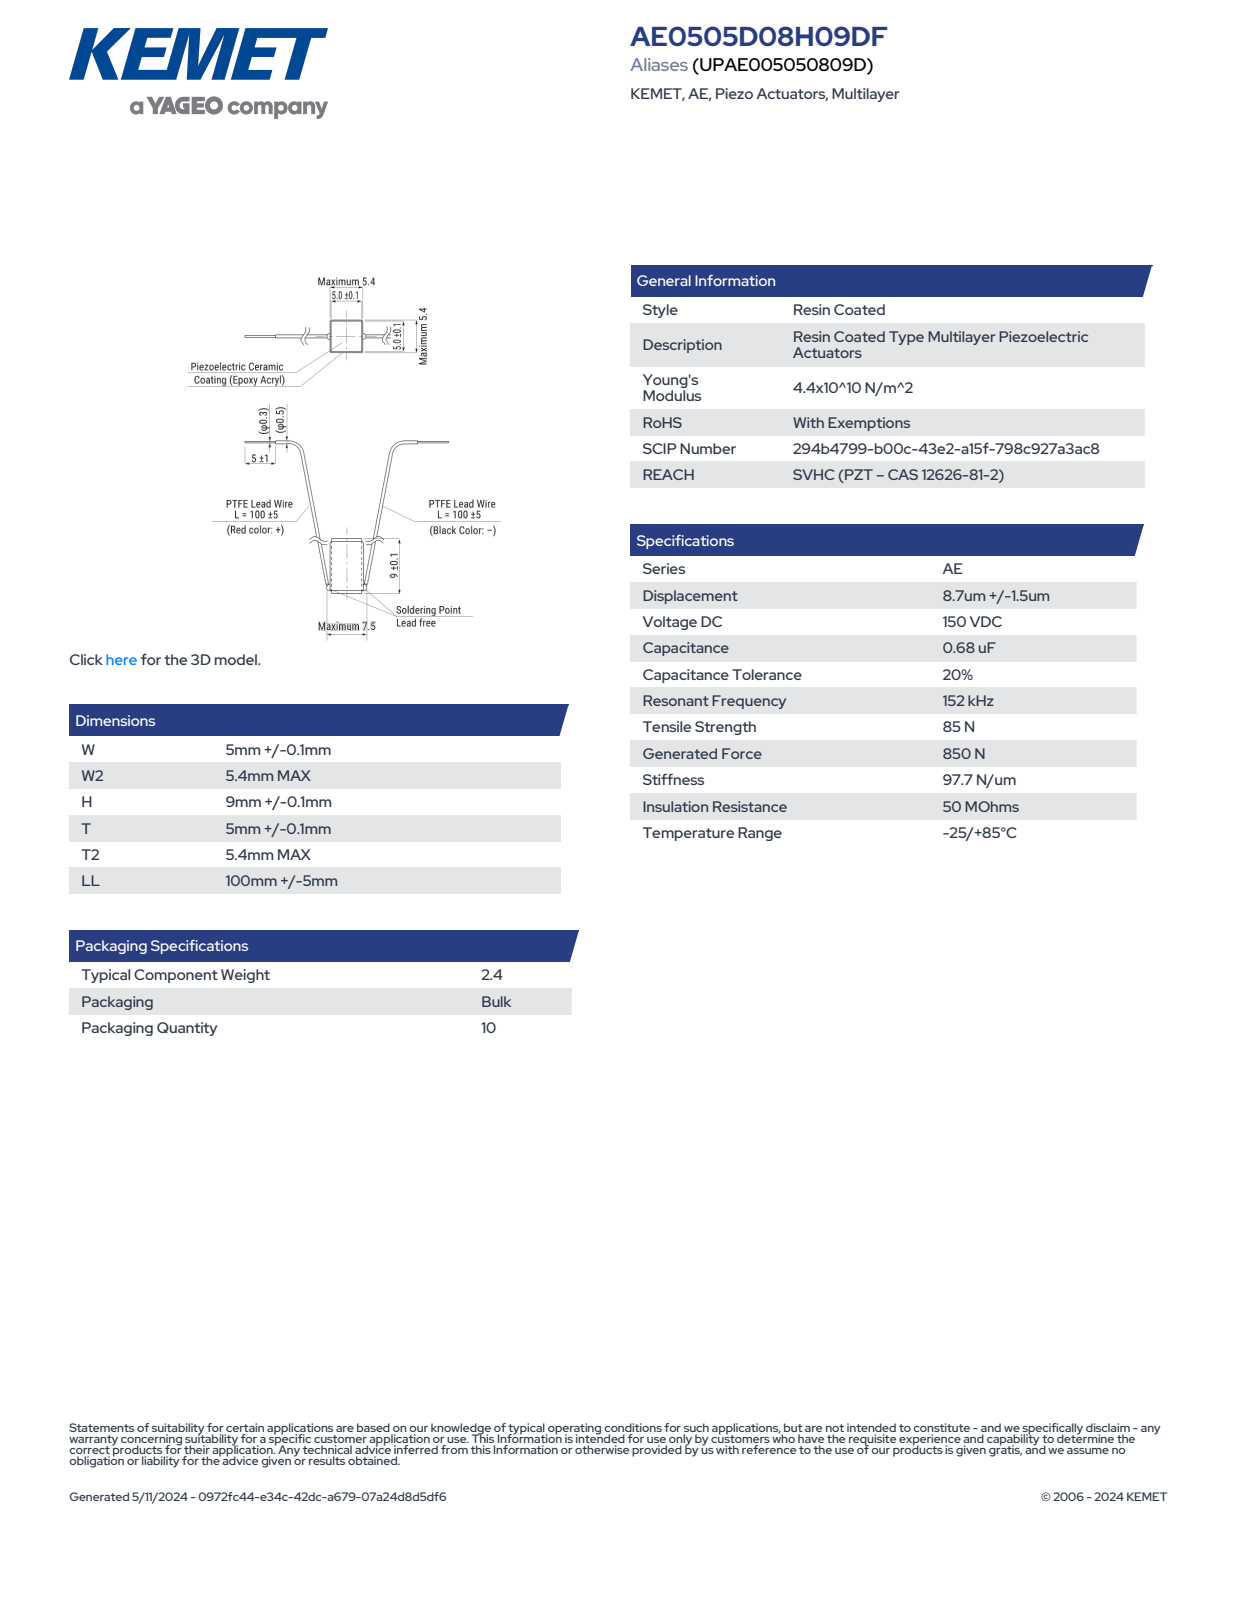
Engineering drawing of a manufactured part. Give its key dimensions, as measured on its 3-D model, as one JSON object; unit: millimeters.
{"part_name": "AL_KAE1_W5.1W25.4H9.1T5.1T25.4", "step_written_by": "SolidWorks 2014 (AUTOMOTIVE_DESIGN)", "units": "millimeters", "bodies": {"solids": 4, "faces": 93, "planar": 85, "cylindrical": 8, "other": 0}, "overall_size": [9.11, 5.4, 5.4], "volume_mm3": 237, "surface_area_mm2": 254, "partial_cylinders_radius": [[0.15, 8]], "face_to_face_distances": [5.1, 5.25, 5, 4.9, 9.1, 5.4, 3.66, 5.44, 0.89, 8.21]}
